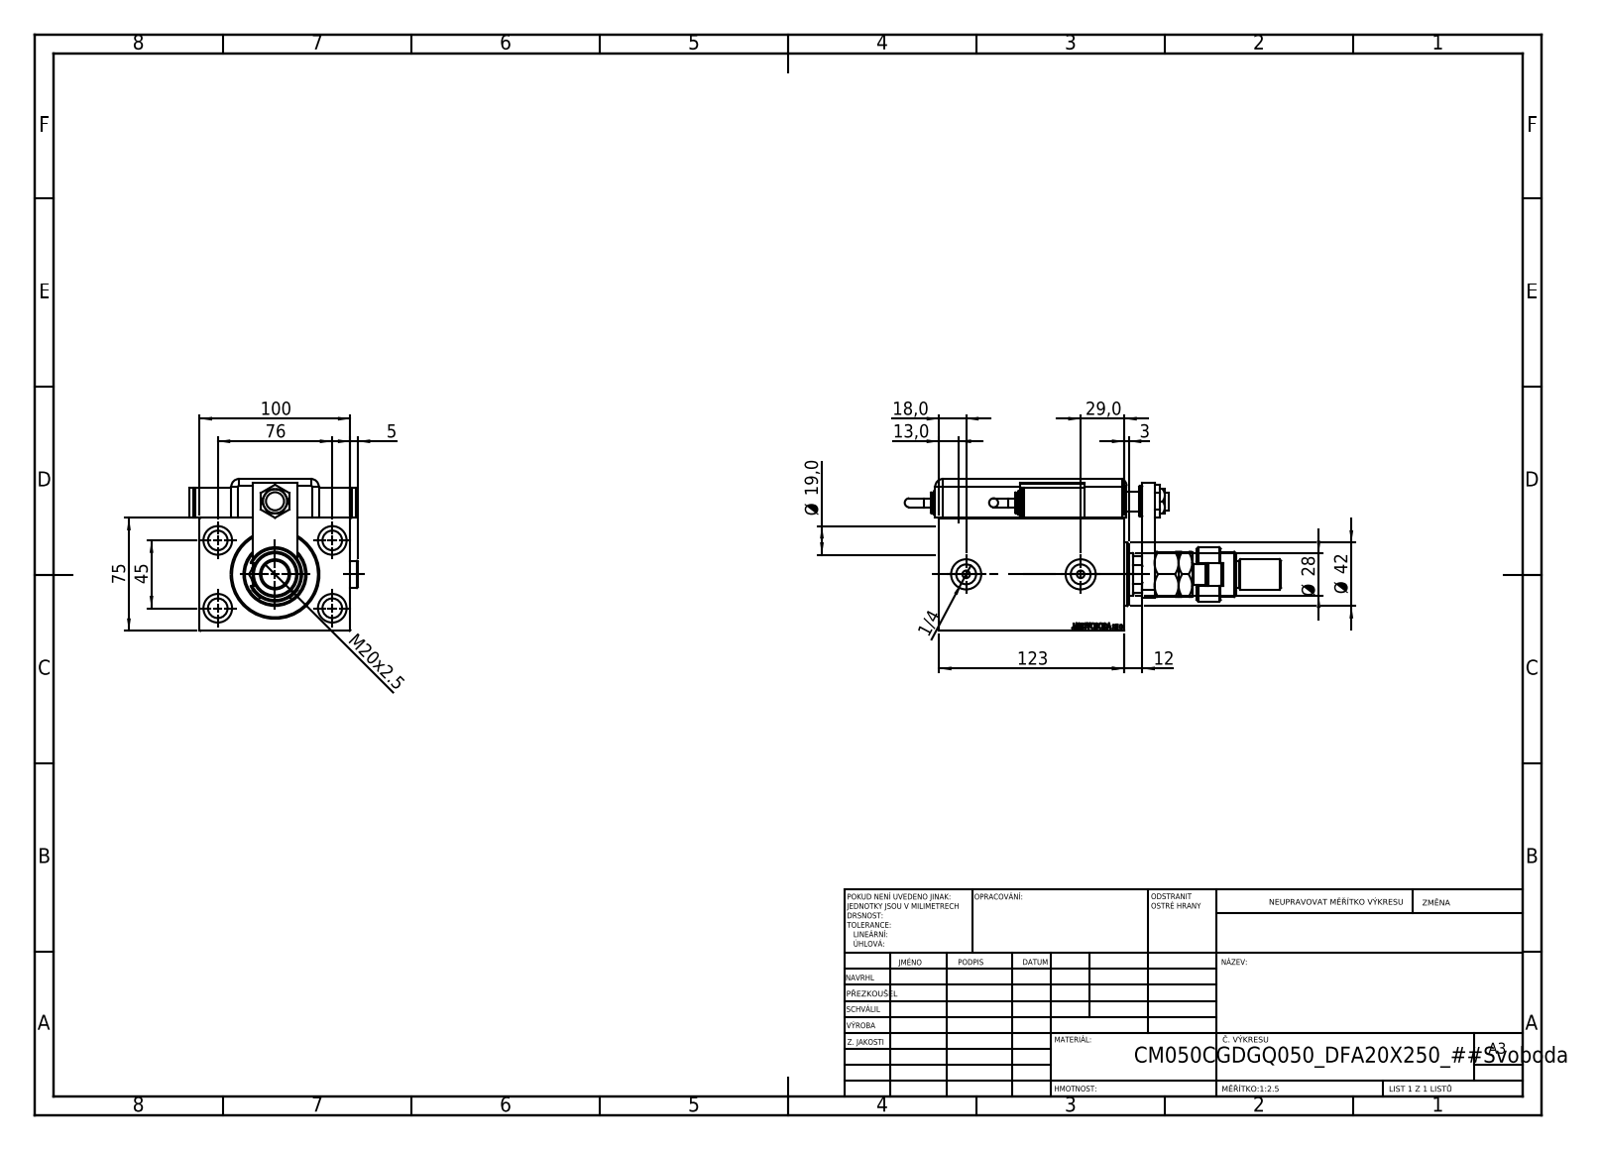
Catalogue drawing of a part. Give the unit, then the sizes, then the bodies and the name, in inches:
Units: inches
Overall size (bounding box): 9.833 × 4.406 × 3.969
Round holes (diameter × count): ⌀0.512 ×5, ⌀0.748 ×4, ⌀0.787 ×3, ⌀0.157 ×2, ⌀0.197 ×2, ⌀0.315 ×2, ⌀0.518 ×2, ⌀0.472 ×1, ⌀0.551 ×1, ⌀0.728 ×1, ⌀1.102 ×1, ⌀1.24 ×1
Round bosses / shafts (diameter × count): ⌀0.787 ×3, ⌀0.709 ×3, ⌀0.551 ×3, ⌀0.63 ×2, ⌀0.236 ×2, ⌀1.654 ×1, ⌀1.417 ×1, ⌀1.181 ×1
Partial cylindrical surfaces — rounded edges, fillets, slot ends (radius × count): R0.197 ×9, R0.295 ×1, R0.394 ×1, R0.472 ×1, R0.531 ×1
Main face-to-face distances: 2.953, 0.118, 3.937, 0.787, 3.969, 1.016, 0.551, 0.531, 4.843, 4.291
Hole centre spacings: 1.739, 2.992, 1.772, 1.813, 3.17, 3.477, 0.787, 1.909
Volume: 59.31 in³ · Surface area: 311.8 in²
Bodies: 17 solids, 1388 faces (677 planar, 146 cylindrical, 565 other)
Part name (STEP PRODUCT): KRYT; V450CM_C_Body; FEMALE_PART_FOR_DFA; SWITCH Q (+7 more)
STEP written by: SolidWorks 2019 (CONFIG_CONTROL_DESIGN)
